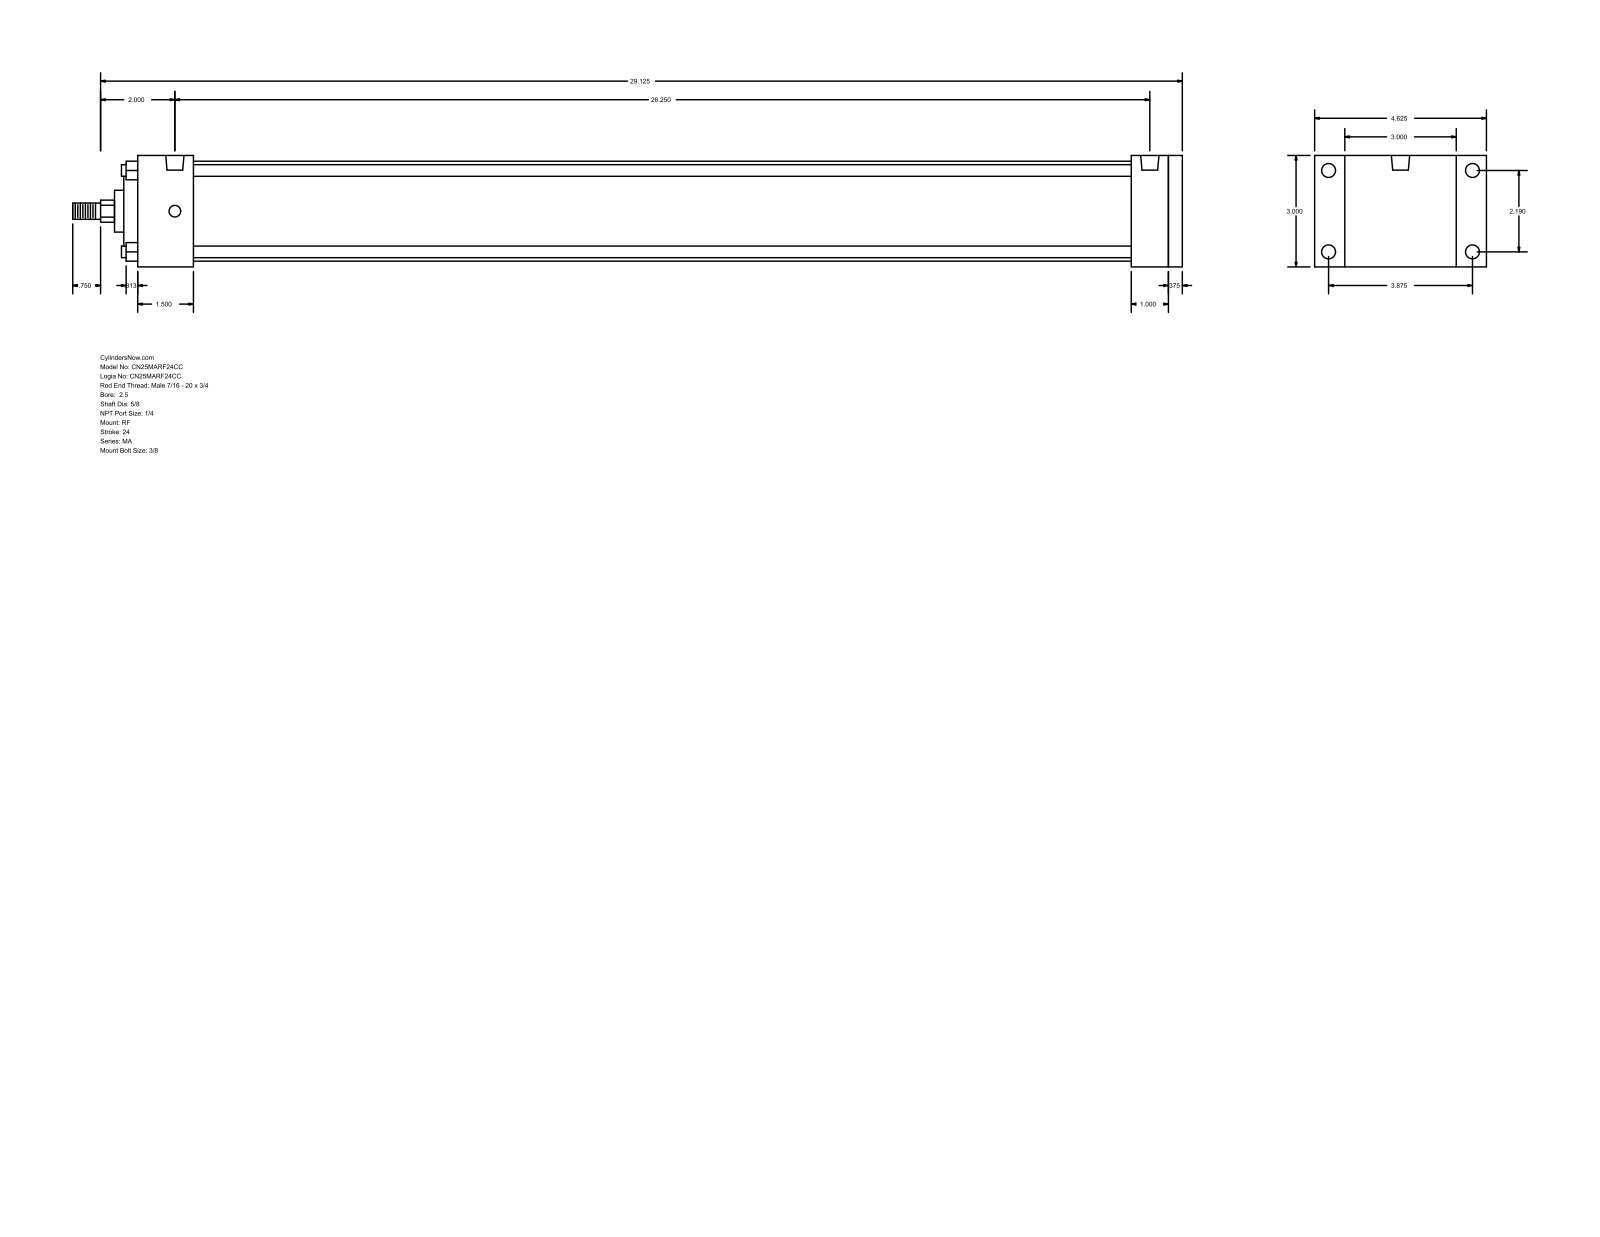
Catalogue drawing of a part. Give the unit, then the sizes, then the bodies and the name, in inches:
Units: inches
Overall size (bounding box): 29.875 × 4.625 × 3
Round holes (diameter × count): ⌀0.313 ×4, ⌀0.375 ×4, ⌀0.492 ×2
Round bosses / shafts (diameter × count): ⌀0.313 ×4, ⌀2.69 ×1, ⌀2 ×1, ⌀1.125 ×1, ⌀0.625 ×1, ⌀0.437 ×1
Partial cylindrical surfaces — rounded edges, fillets, slot ends (radius × count): R0.297 ×1
Main face-to-face distances: 3, 28.125, 0.375, 27.75, 1, 1.5, 26.75, 25.25, 26.25, 26.625
Hole centre spacings: 2.19, 3.875, 4.451, 26.25
Bodies: 0 solids, 94 faces (65 planar, 29 cylindrical, 0 other)
Part name (STEP PRODUCT): MA_RF__0250_0.625
STEP written by: GSSL Pune (CONFIG_CONTROL_DESIGN)
